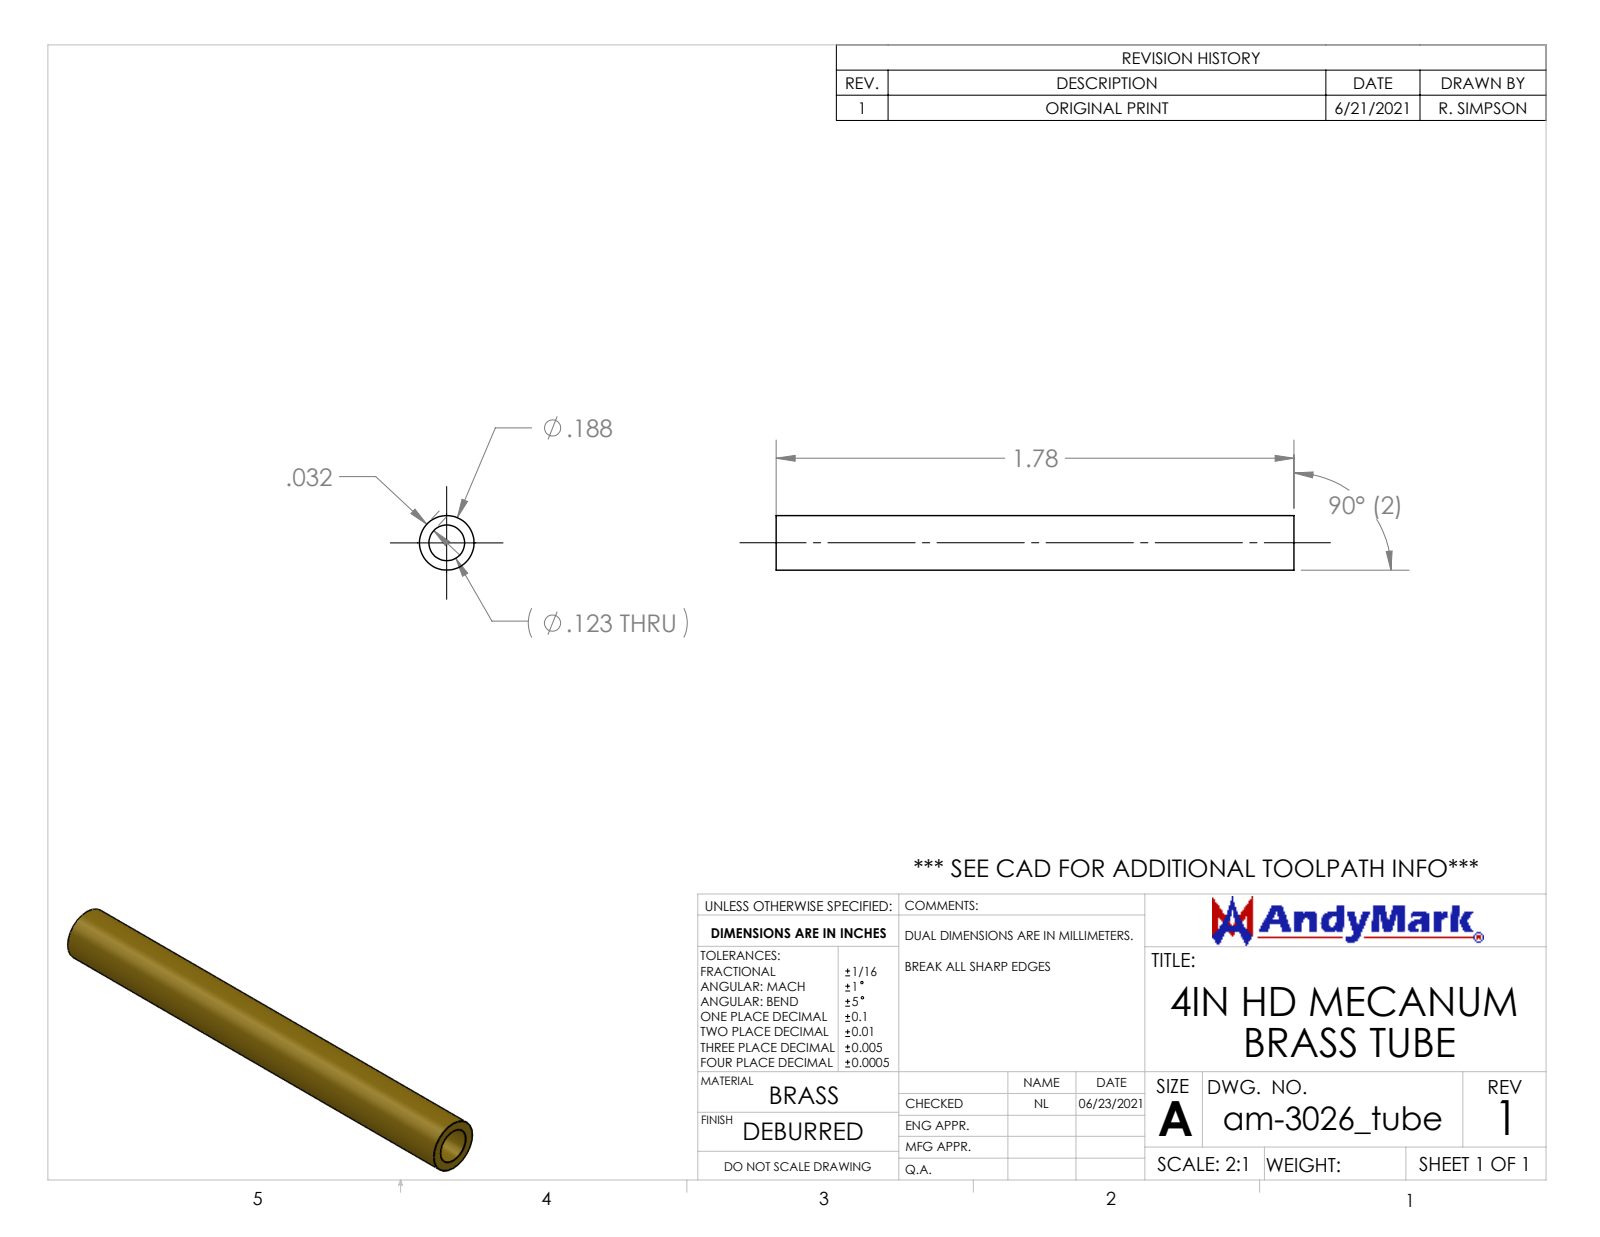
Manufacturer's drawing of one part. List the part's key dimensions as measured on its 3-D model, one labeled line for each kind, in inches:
Part name (STEP PRODUCT): Brass tube
STEP written by: SolidWorks 2021 (AUTOMOTIVE_DESIGN)
Units: inches
Bodies: 1 solid, 6 faces (2 planar, 4 cylindrical, 0 other)
Overall size (bounding box): 1.78 × 0.188 × 0.188
Volume: 0.028 in³ · Surface area: 1.768 in²
Round holes (diameter × count): ⌀0.123 ×1
Round bosses / shafts (diameter × count): ⌀0.187 ×1
Main face-to-face distances: 1.78
